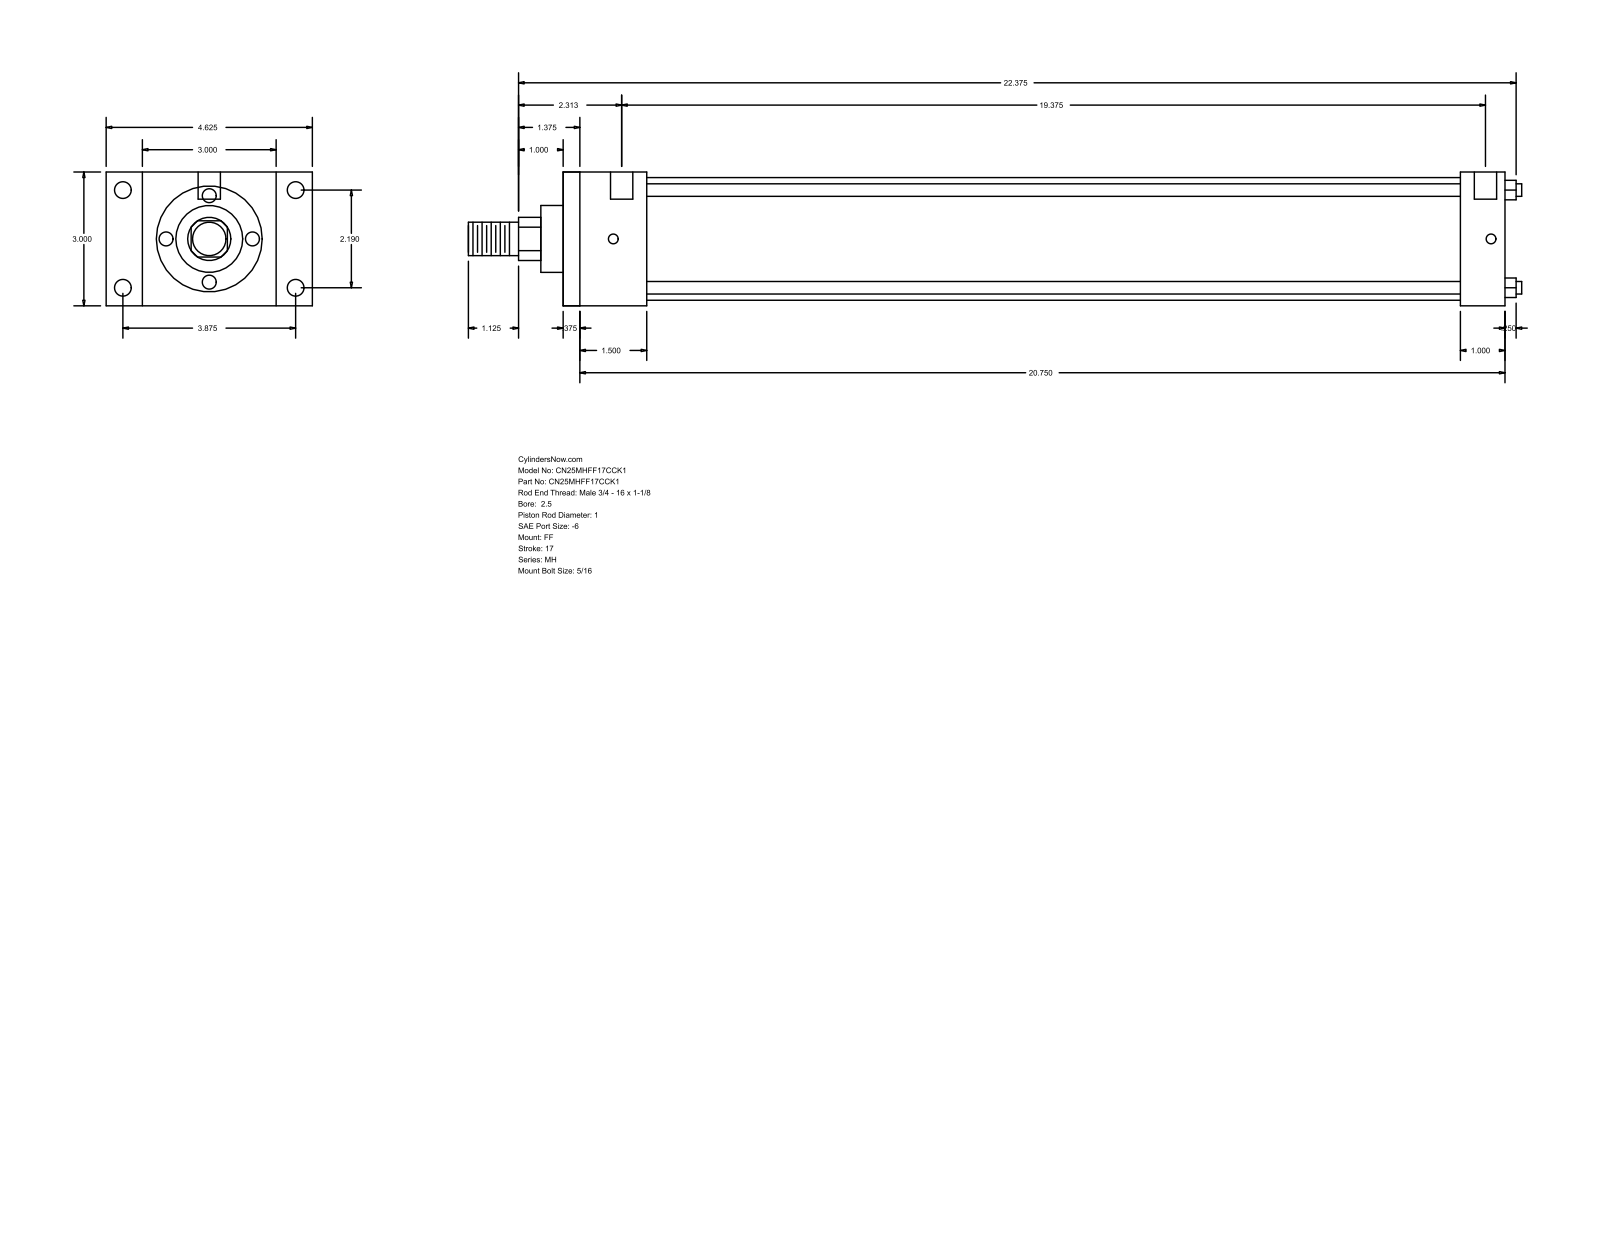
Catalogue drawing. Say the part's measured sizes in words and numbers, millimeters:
The part is named "MH_FF__0250_1". Its 3-D file was written by "GSSL Pune (CONFIG_CONTROL_DESIGN)". It is 0 solids with 92 faces: 64 planar, 28 cylindrical and 0 other. Overall it measures 600.08 by 117.47 by 76.2 millimeters. Round holes: 4 of diameter 5.56, 4 of diameter 9.53, 2 of diameter 12.7. Round bosses or shafts: 4 of diameter 7.14, 1 of diameter 69.85, 1 of diameter 38.1, 1 of diameter 25.4, 1 of diameter 19.05. Partial cylindrical surfaces (rounded edges, fillets, slot ends): 1 of radius 12.29. The main face-to-face distances are 76.2, 536.58, 9.52, 527.06, 25.4, 47.63, 511.18, 38.11, 501.66, 463.55. The hole center spacings are 55.62, 98.42, 113.05, 500.06, 3.18, 4.76, 492.12, 495.3.
